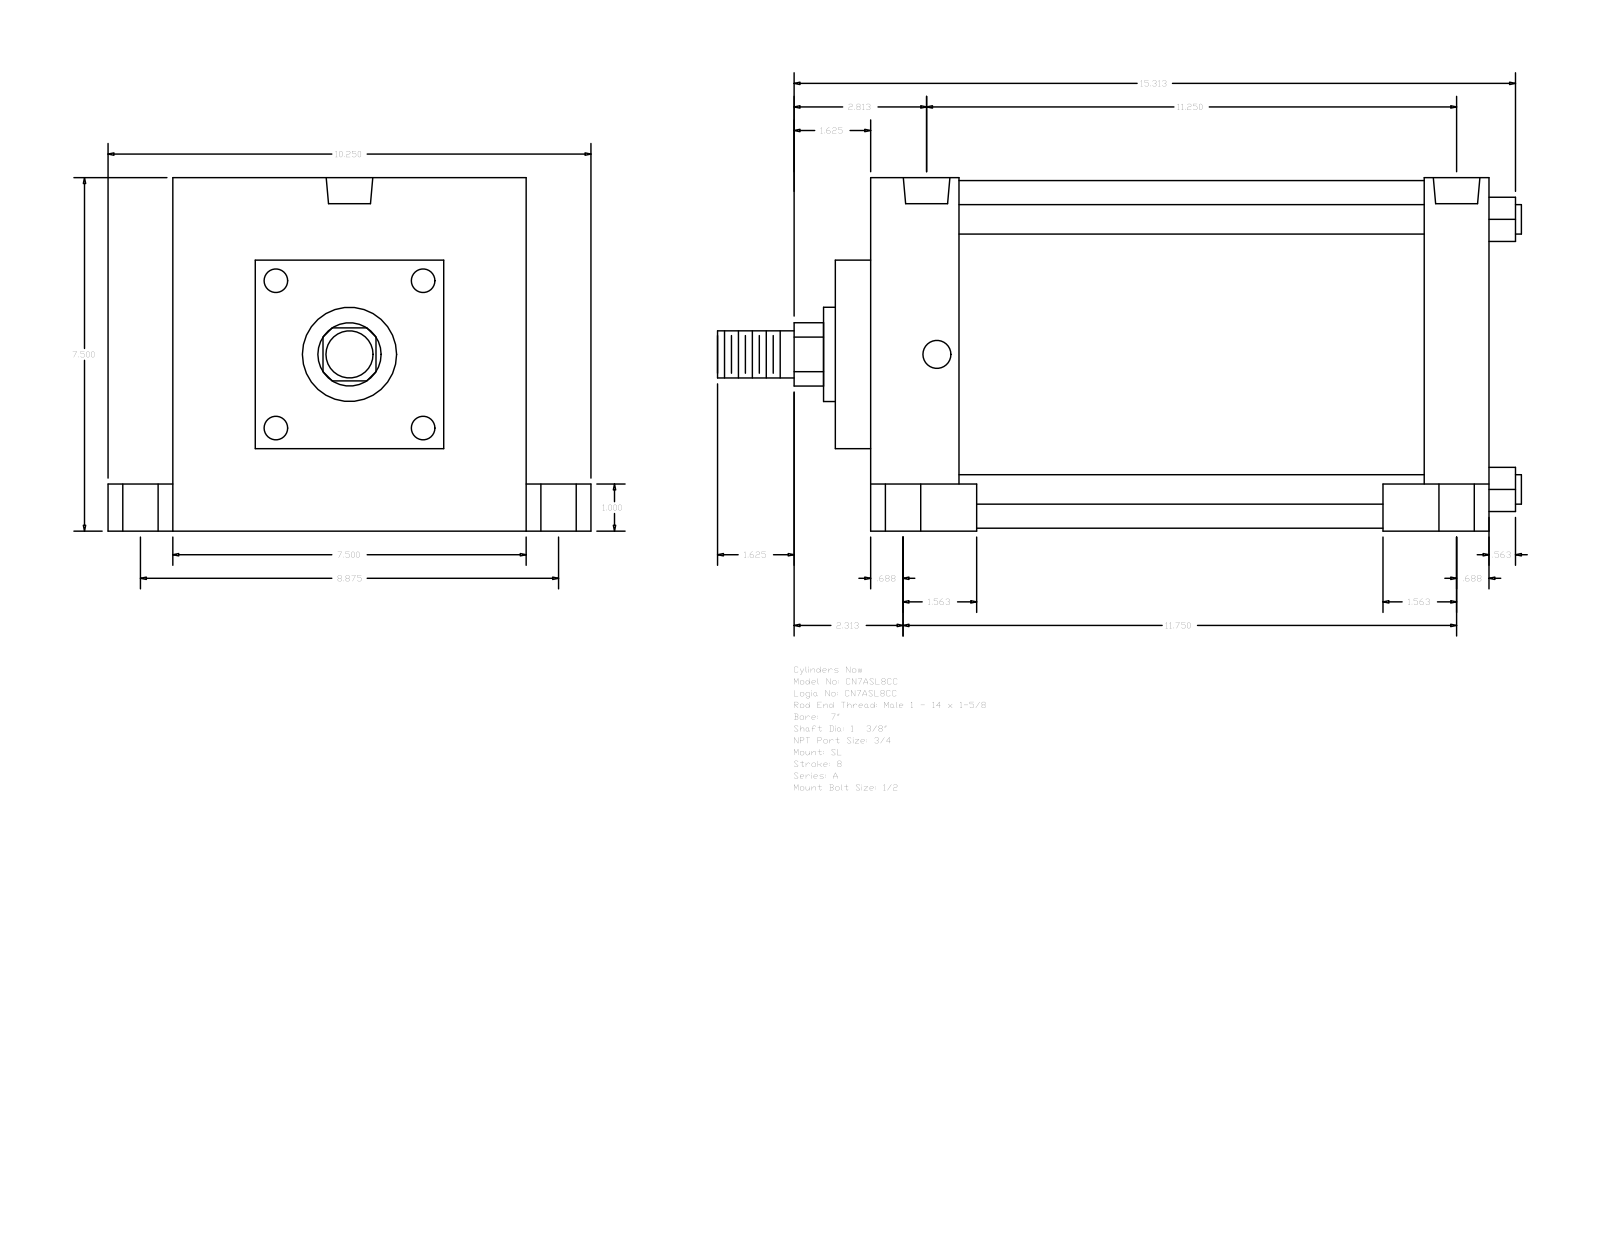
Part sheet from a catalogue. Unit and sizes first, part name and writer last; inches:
Units: inches
Overall size (bounding box): 17.063 × 10.25 × 7.5
Round holes (diameter × count): ⌀0.594 ×4, ⌀0.75 ×4, ⌀1 ×4, ⌀0.989 ×2
Round bosses / shafts (diameter × count): ⌀0.625 ×4, ⌀7.375 ×1, ⌀2 ×1, ⌀1.375 ×1, ⌀1 ×1
Partial cylindrical surfaces — rounded edges, fillets, slot ends (radius × count): R0.672 ×1
Main face-to-face distances: 7.5, 13.125, 0.75, 13.875, 12.5, 2.625, 1.875, 11.25, 11.75, 9.875
Hole centre spacings: 0.219, 4.437, 4.443, 4.465, 4.495, 8.875, 10.812, 11.031
Bodies: 0 solids, 117 faces (85 planar, 32 cylindrical, 0 other)
Part name (STEP PRODUCT): A_SL__0700_1.375
STEP written by: GSSL Pune (CONFIG_CONTROL_DESIGN)
